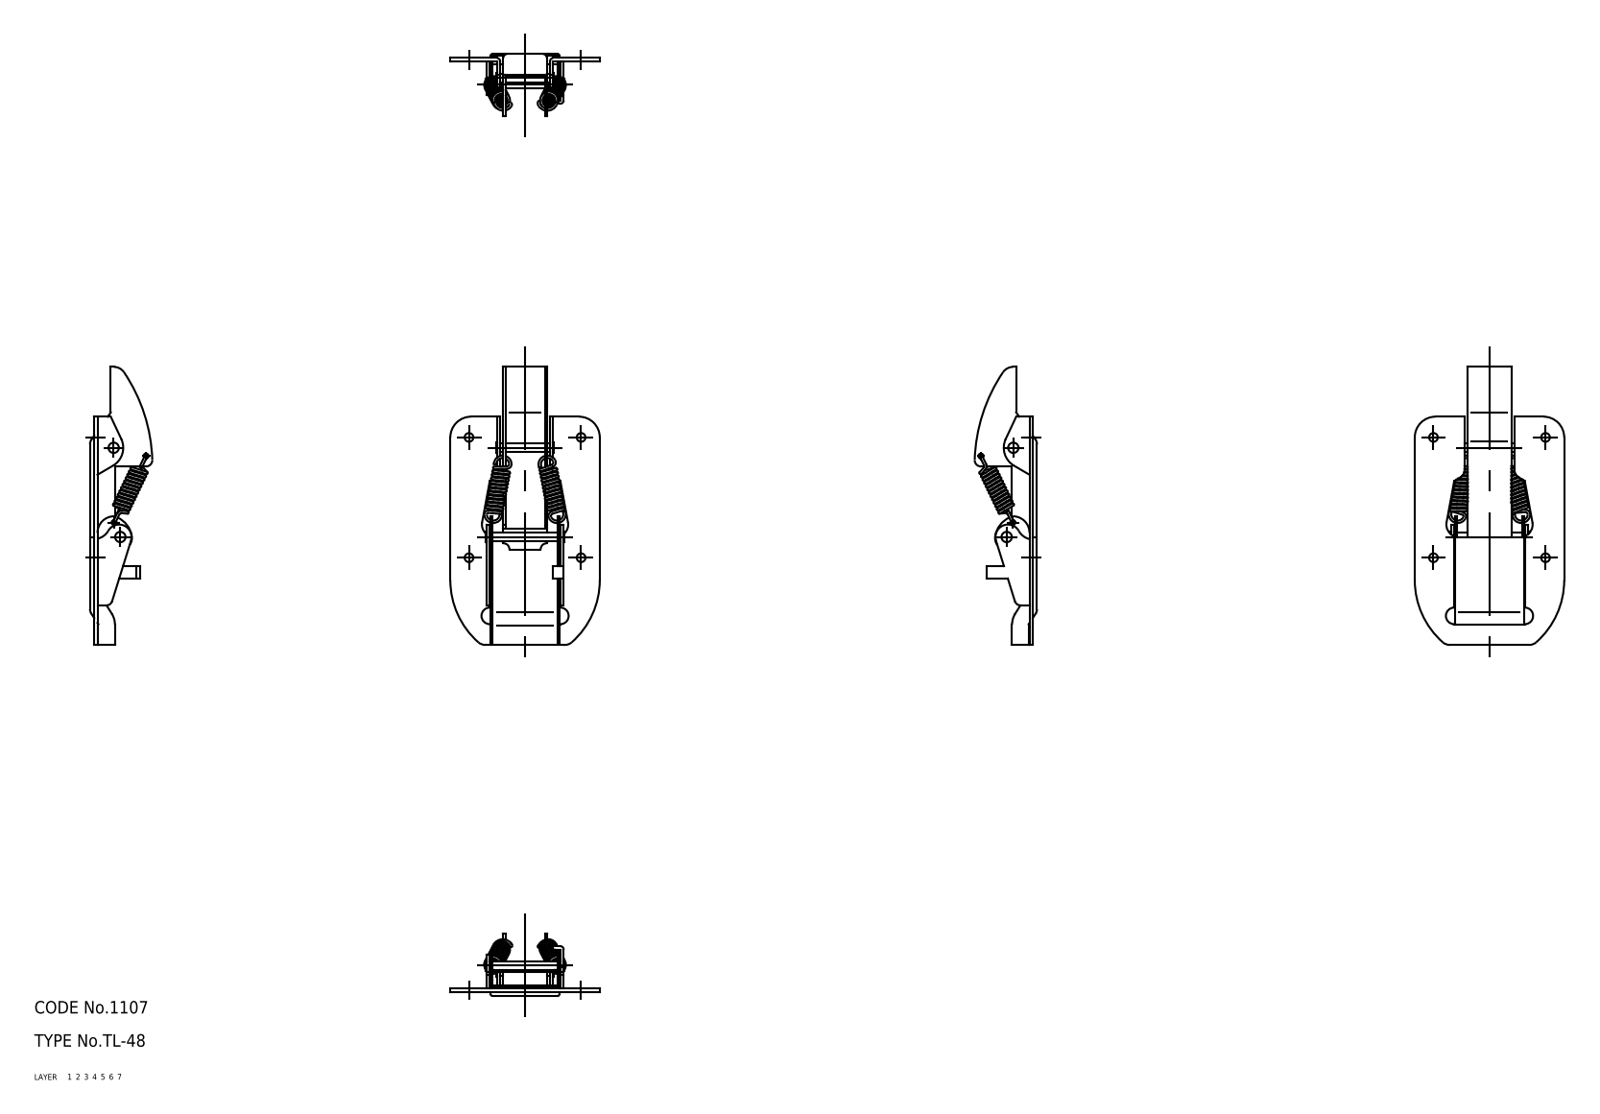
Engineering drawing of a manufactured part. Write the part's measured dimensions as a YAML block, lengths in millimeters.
part_name: "spring_mr; spring; arm; base (+2 more)"
step_written_by: "CADfix (AUTOMOTIVE_DESIGN)"
units: millimeters
bodies: {solids: 5, faces: 257, planar: 0, cylindrical: 0, other: 257}
overall_size: [67, 36, 15]
volume: 2832
surface_area: 7847
